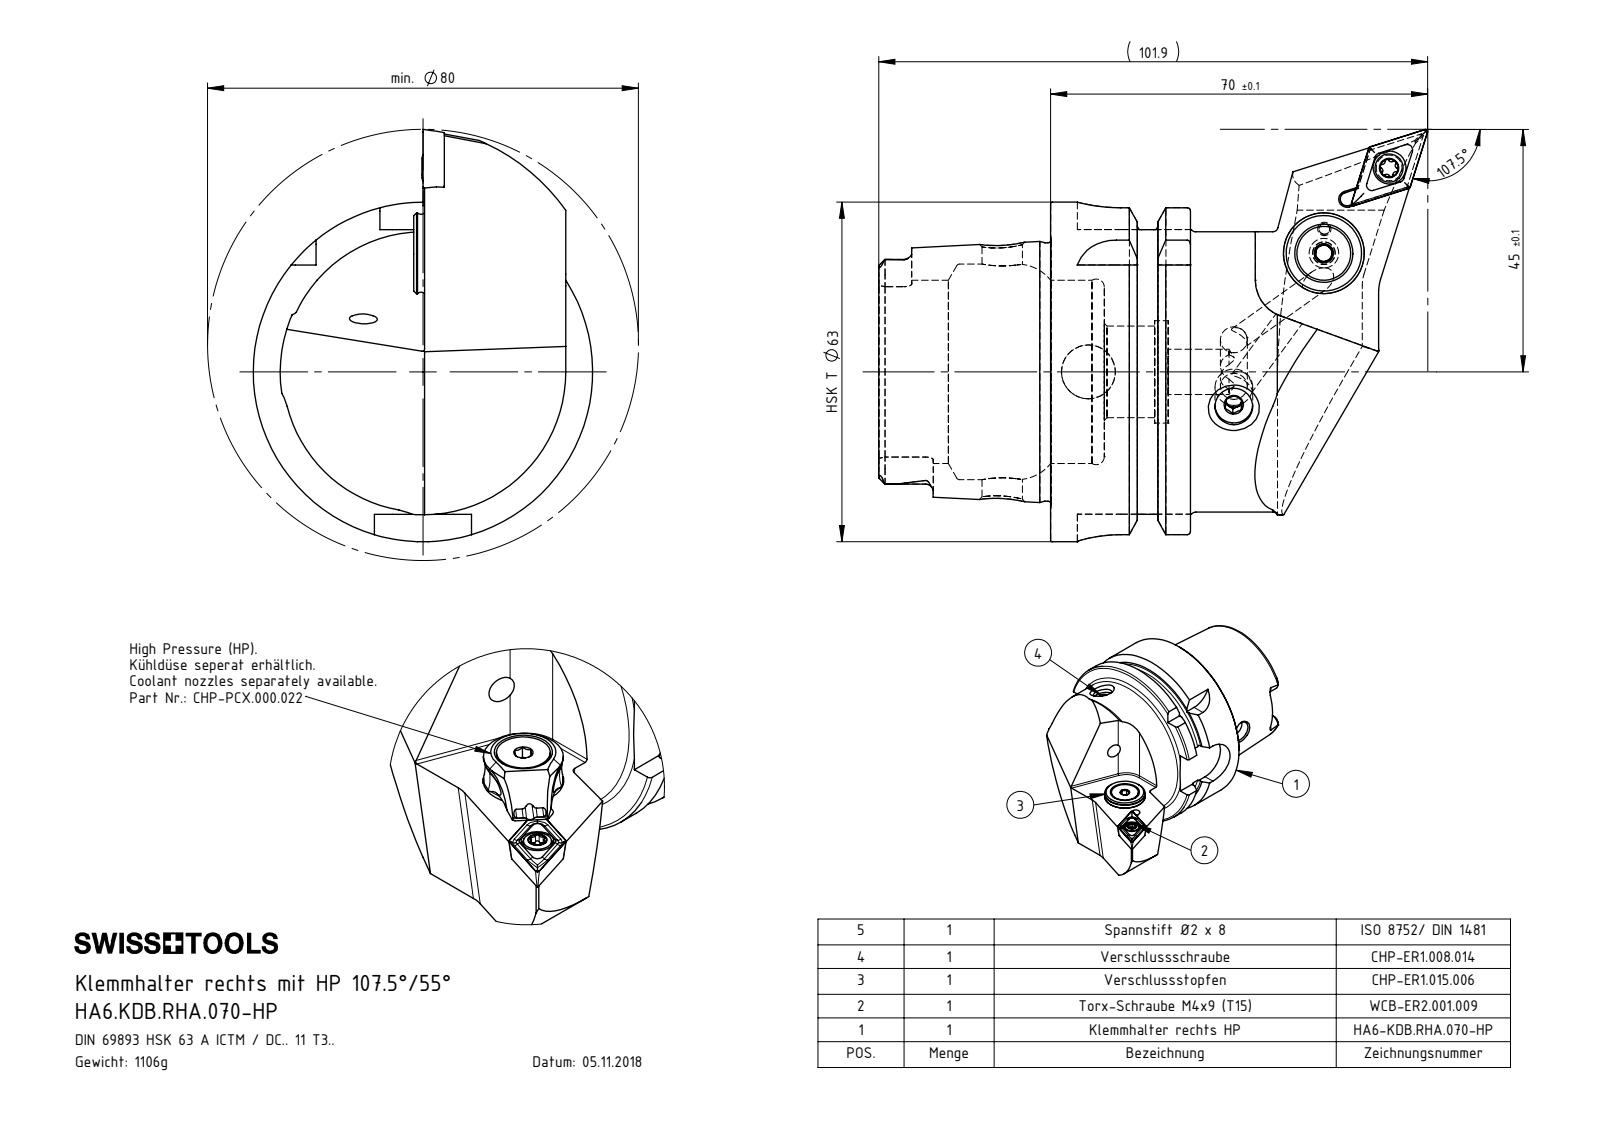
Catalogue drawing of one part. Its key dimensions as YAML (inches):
part_name: "CHP-PCX.000.022_B; DCMT11T304; DIN 3771 - 6.5x1.5; DIN 3771 - 13x1 (+7 more)"
step_written_by: "SolidWorks 2017 (AUTOMOTIVE_DESIGN)"
units: inches
bodies: {solids: 9, faces: 517, planar: 131, cylindrical: 152, other: 234}
overall_size: [4.012, 3.012, 2.48]
volume: 8.607
surface_area: 51.81
round_holes:
  - {diameter: 0.165, count: 2}
  - {diameter: 0.197, count: 2}
  - {diameter: 0.047, count: 1}
  - {diameter: 0.079, count: 1}
  - {diameter: 0.118, count: 1}
  - {diameter: 0.13, count: 1}
  - {diameter: 0.173, count: 1}
  - {diameter: 0.209, count: 1}
  - {diameter: 0.24, count: 1}
  - {diameter: 0.276, count: 1}
  - {diameter: 0.295, count: 1}
  - {diameter: 0.331, count: 1}
round_bosses_or_shafts:
  - {diameter: 2.48, count: 1}
  - {diameter: 2.163, count: 1}
  - {diameter: 2.047, count: 1}
  - {diameter: 1.887, count: 1}
  - {diameter: 0.585, count: 1}
  - {diameter: 0.528, count: 1}
  - {diameter: 0.394, count: 1}
  - {diameter: 0.315, count: 1}
partial_cylinders:
  - {radius: 0.039, count: 7}
  - {radius: 0.013, count: 6}
  - {radius: 0.023, count: 6}
  - {radius: 0.055, count: 6}
  - {radius: 0.02, count: 4}
  - {radius: 0.315, count: 4}
  - {radius: 0.236, count: 3}
  - {radius: 0.043, count: 2}
face_to_face_distances: [1.022, 0.63, 0.392, 1.031, 1.256, 1.648, 2.278, 2.079, 0.858, 0.467]
hole_center_spacings: [0.177, 0.65, 0.656, 0.784, 0.789, 1.927, 2.015, 2.655]
